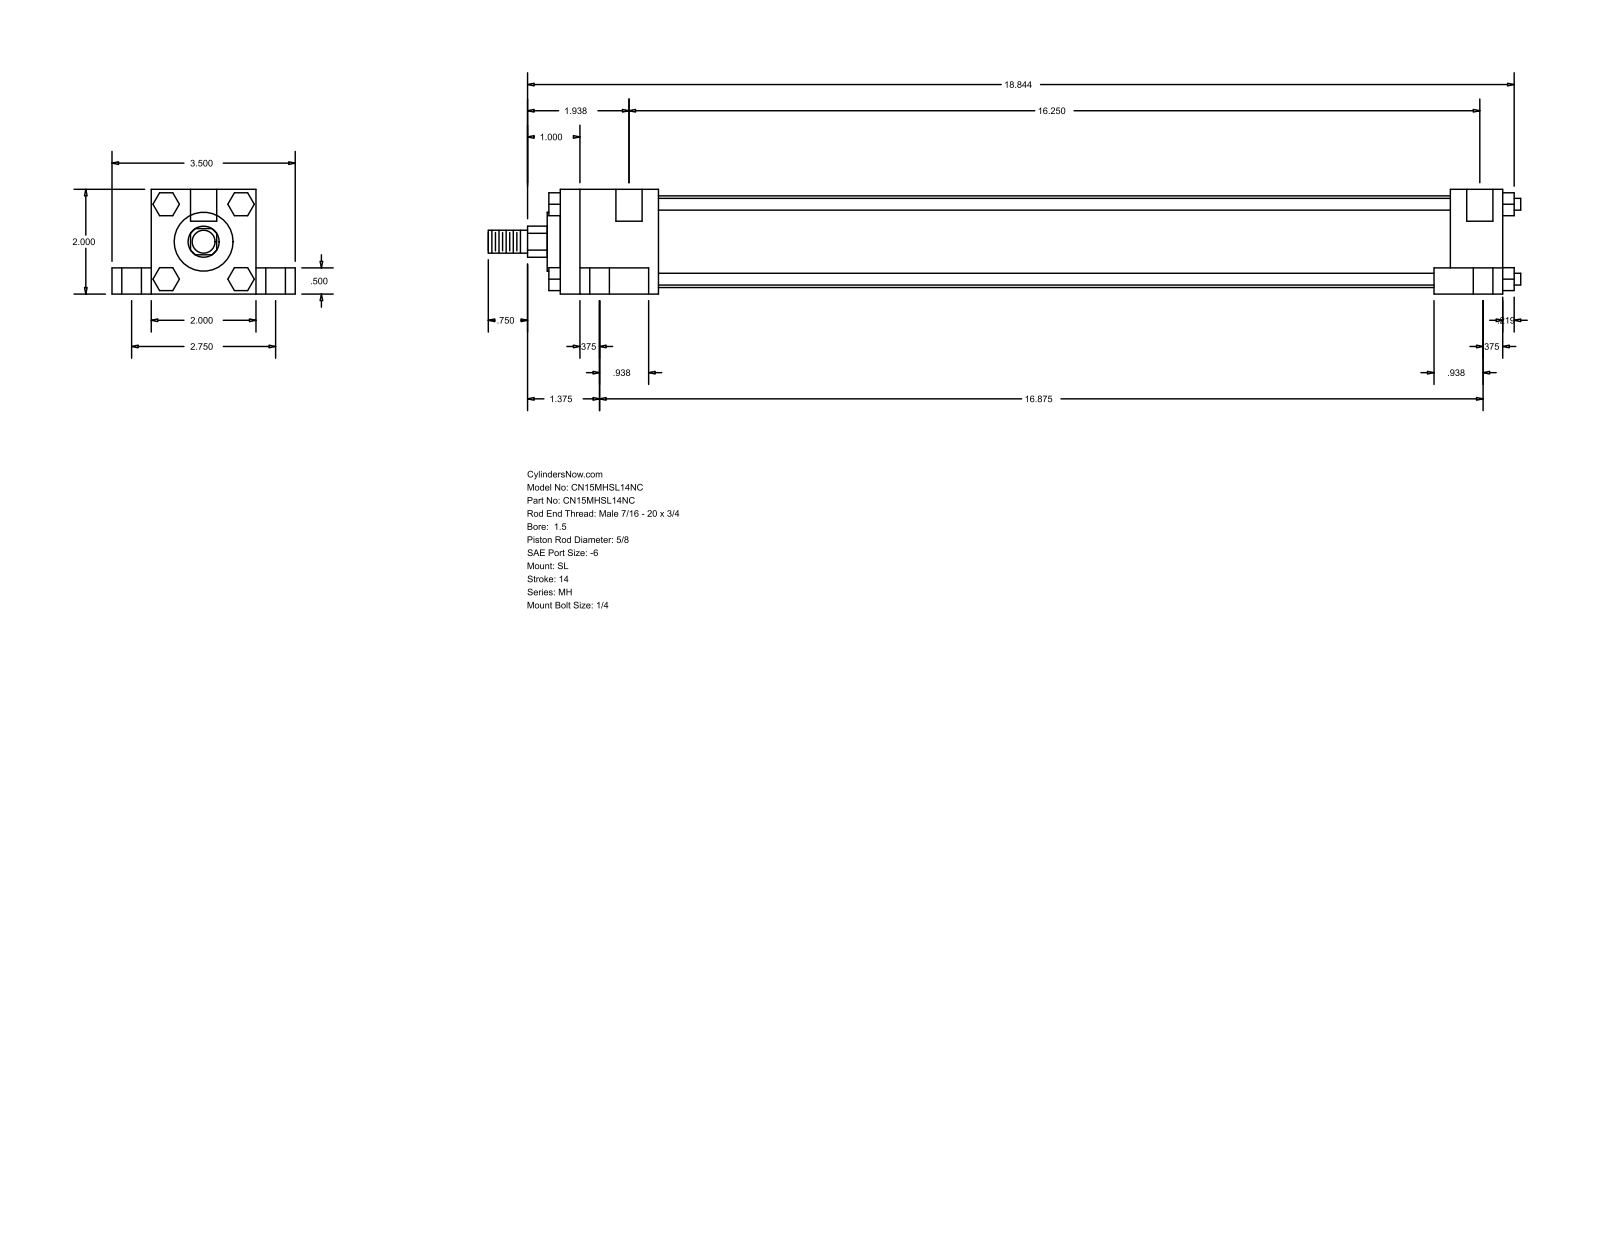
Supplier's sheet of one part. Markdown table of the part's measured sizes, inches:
| quantity | value |
| --- | --- |
| part name | MH_SL__0150_0.625 |
| STEP written by | GSSL Pune (CONFIG_CONTROL_DESIGN) |
| units | inches |
| bodies | 0 solids, 148 faces (112 planar, 36 cylindrical, 0 other) |
| overall size | 19.719 × 3.5 × 2 |
| round holes (diameter × count) | 0.219 × 4, 0.375 × 4, 0.625 × 4, 0.5 × 2 |
| round bosses / shafts (diameter × count) | 0.225 × 4, 1.75 × 1, 1.125 × 1, 0.625 × 1, 0.437 × 1 |
| partial cylindrical surfaces (radius × count) | 0.297 × 1 |
| main face-to-face distances | 2, 1.5, 0.75, 0.5, 2.75, 18, 0.375, 17, 1, 1.875 |
| hole center spacings | 1.376, 1.443, 1.485, 2.75, 16.37, 16.375, 16.495, 16.869 |
